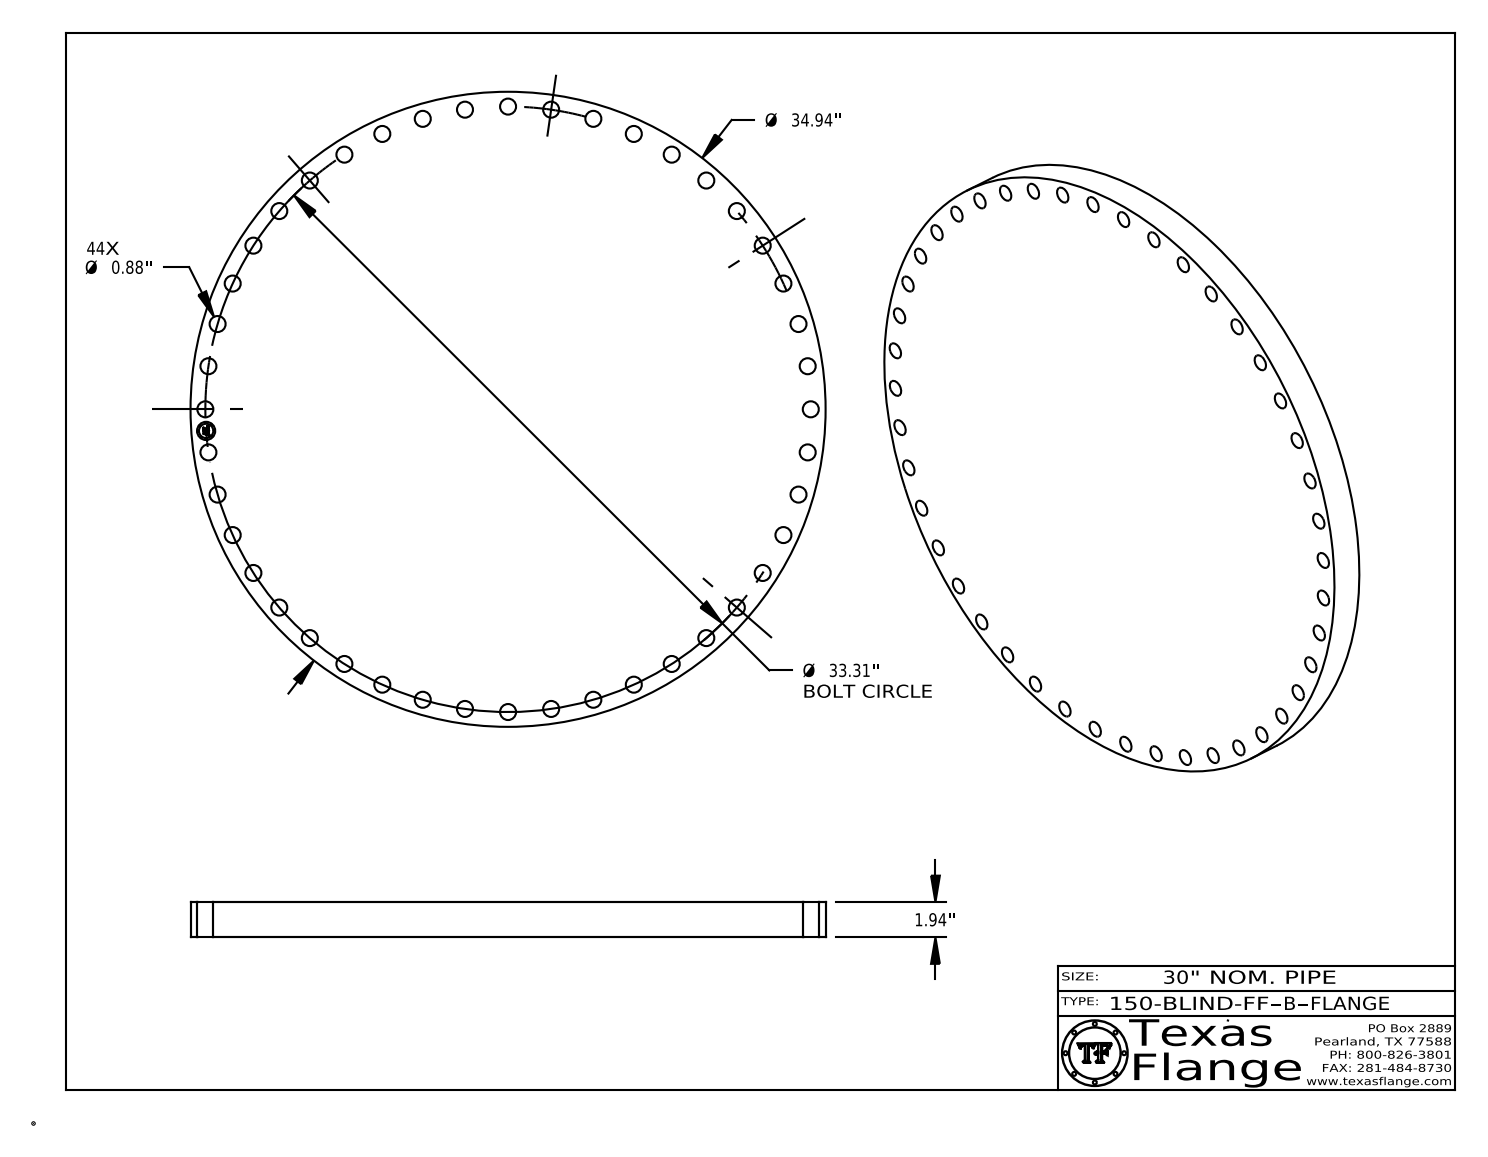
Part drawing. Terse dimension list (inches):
name: 150-BLIND-FF, Series B
written by: CATIA V5 STEP AP214 (AUTOMOTIVE_DESIGN)
unit: in
bodies: 1 solid, 477 faces (367 planar, 110 cylindrical, 0 other)
size: 34.94 × 34.94 × 1.94
volume: 1 808 in³; area: 2 313 in²
holes: 44× ⌀0.88, 1× ⌀1
bosses: 8× ⌀0.061, 1× ⌀34.94, 1× ⌀0.788
face distances: 1.94, 0.015, 1.925, 0.298, 0.292, 0.054, 0.193, 0.248, 0.044, 0.15
hole spacings: 2.376, 33.225, 31.961, 32.971, 4.741, 32.549, 11.641, 15.964
